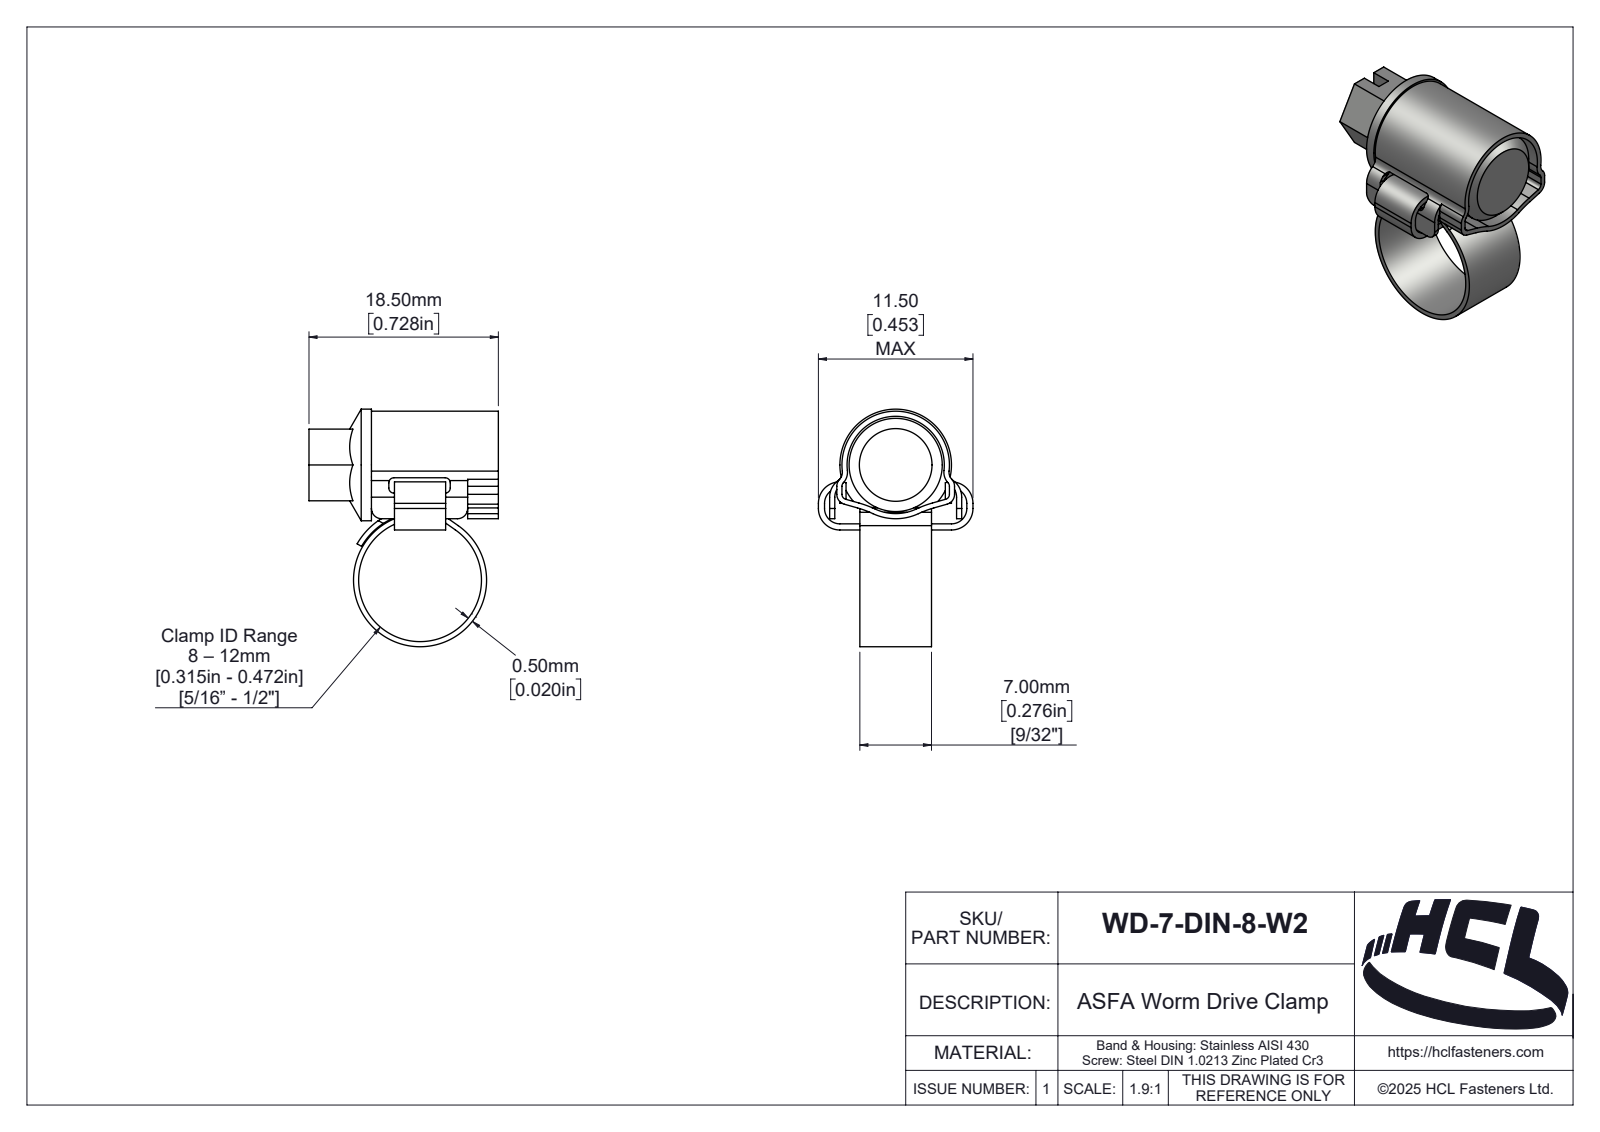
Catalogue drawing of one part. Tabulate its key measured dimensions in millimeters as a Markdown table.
| quantity | value |
| --- | --- |
| part name | WD-7-DIN-8-W2 |
| STEP written by | SolidWorks 2025 (AUTOMOTIVE_DESIGN) |
| units | millimeters |
| bodies | 4 solids, 245 faces (74 planar, 118 cylindrical, 53 other) |
| overall size | 23.2 × 18.5 × 15.1 |
| volume | 1 512 mm³ |
| surface area | 2 445 mm² |
| round holes (diameter × count) | 12 × 1 |
| round bosses / shafts (diameter × count) | 13 × 1, 10.9 × 1, 9.1 × 1 |
| partial cylindrical surfaces (radius × count) | 0.5 × 8, 1 × 8, 1.5 × 8, 2.1 × 4, 2 × 3, 3 × 2, 10 × 2, 10.5 × 2 |
| main face-to-face distances | 0.5, 12.4, 0.6, 2.85, 6.1, 7, 2.95, 2.45, 9.45, 9.95 |
